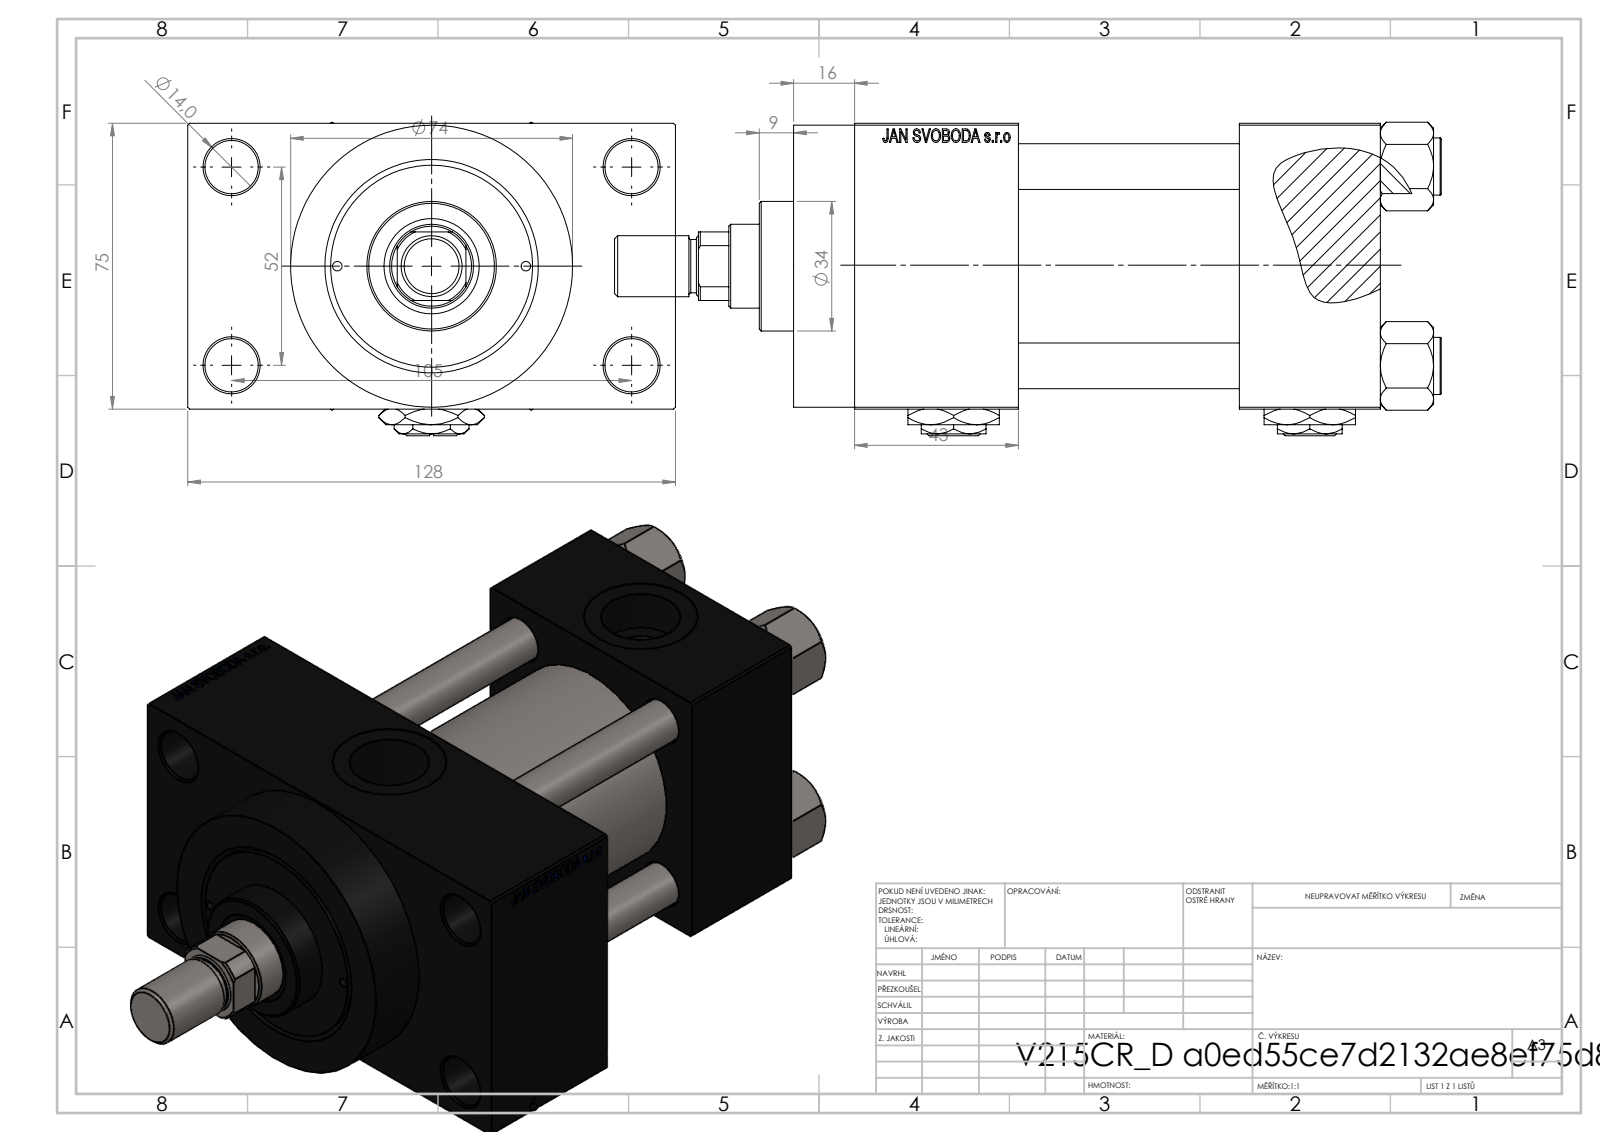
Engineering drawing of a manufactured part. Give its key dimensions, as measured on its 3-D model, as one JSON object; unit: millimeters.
{"part_name": "V215CR_D_Body; V215CR_VCP_D; NUT_M5_D; V215CR_D_TYCINKA (+3 more)", "step_written_by": "SolidWorks 2019 (CONFIG_CONTROL_DESIGN)", "units": "millimeters", "bodies": {"solids": 14, "faces": 1227, "planar": 551, "cylindrical": 108, "other": 568}, "overall_size": [217, 128, 82.27], "volume_mm3": 806247, "surface_area_mm2": 170659, "round_holes": [[12, 4], [14, 4], [2.5, 2], [7, 2], [20.96, 2], [30, 2], [10.5, 1], [22, 1], [25, 1], [41, 1], [50, 1], [53, 1]], "round_bosses_or_shafts": [[15, 4], [74, 1], [56, 1], [34, 1], [16, 1], [14, 1]], "partial_cylinders_radius": [[10.5, 1]], "face_to_face_distances": [75, 58, 37, 95, 26.5, 101.5, 101, 138, 43, 16], "hole_center_spacings": [26.19, 26.35, 36.98, 38.03, 52.3, 57.22, 58.43, 58.59]}
